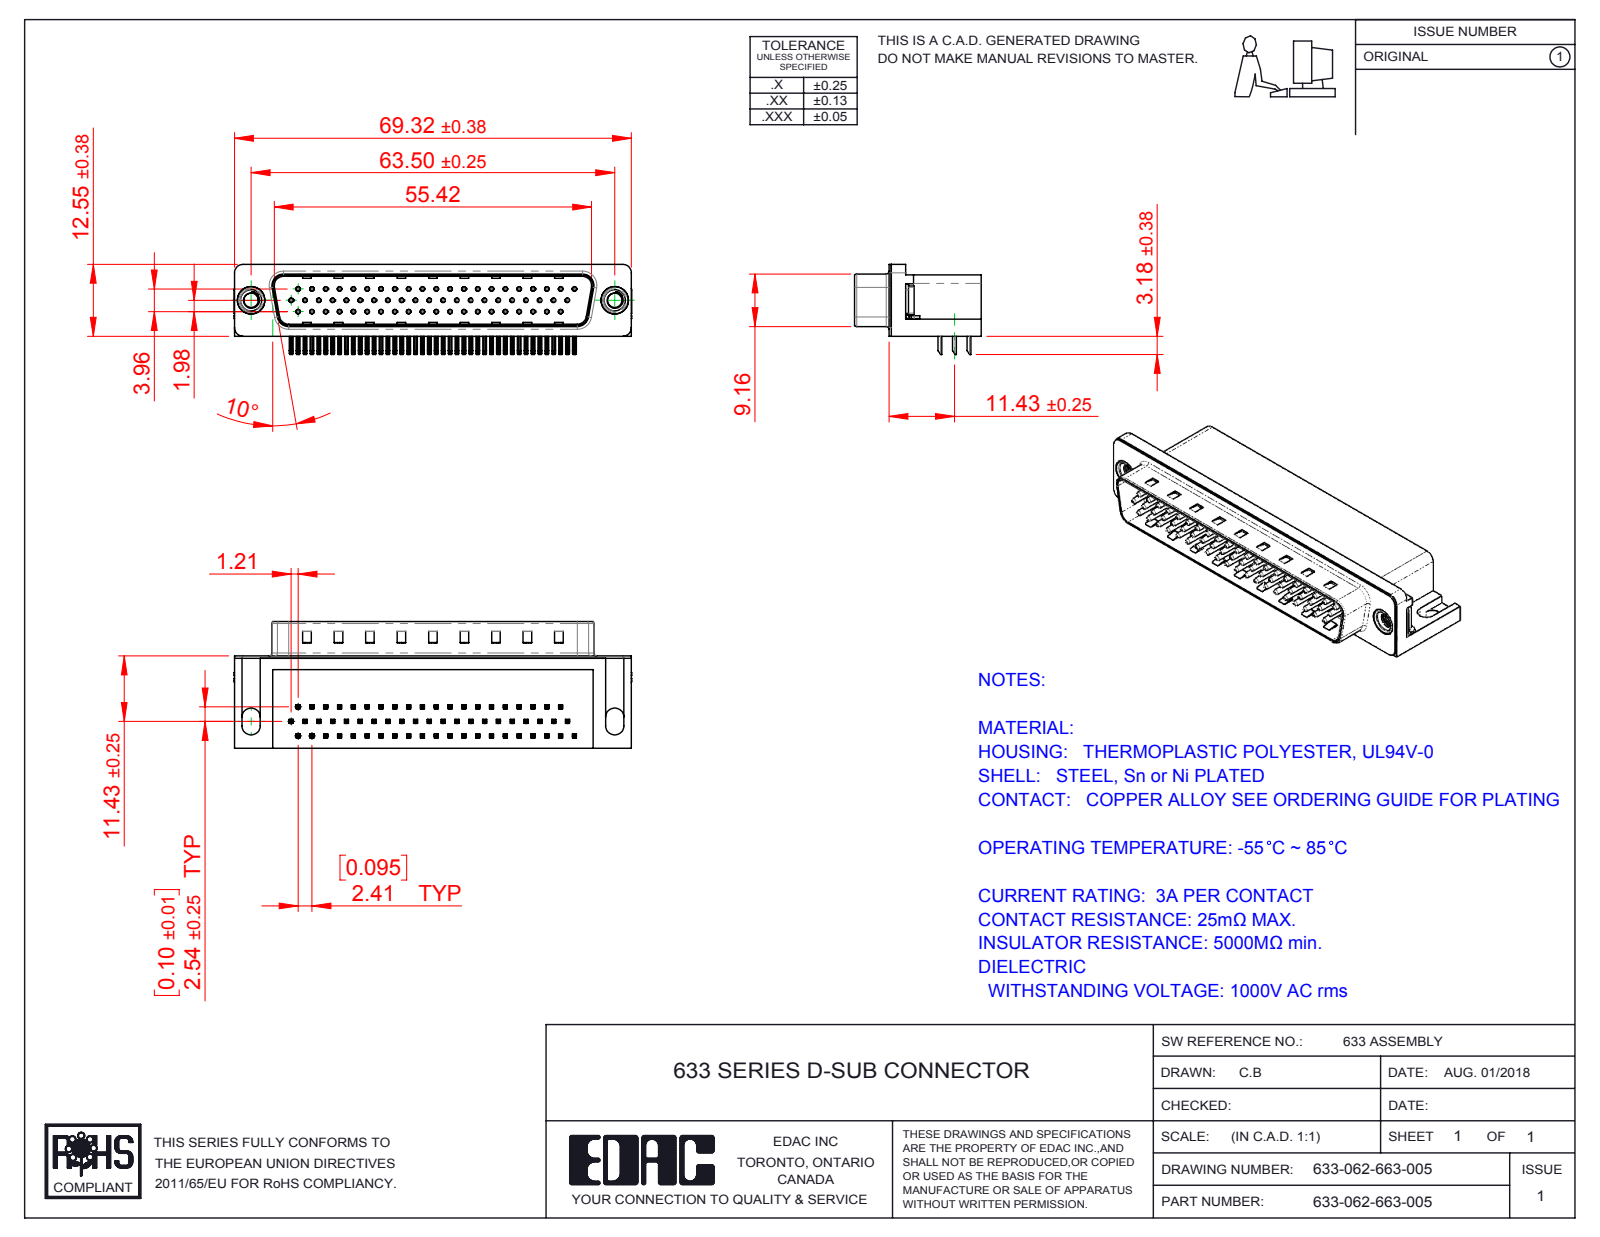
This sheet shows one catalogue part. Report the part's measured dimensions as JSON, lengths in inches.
{"part_name": "633 Housing_62 Contact; 633 M3 Threaded Rivet; 633-062-663-005; 633 Contact Bottom (+4 more)", "step_written_by": "SolidWorks 2016 (CONFIG_CONTROL_DESIGN)", "units": "inches", "bodies": {"solids": 68, "faces": 5072, "planar": 3213, "cylindrical": 1442, "other": 417}, "overall_size": [2.732, 0.87, 0.619], "volume_in3": 0.671, "surface_area_in2": 20.44, "round_holes": [[0.014, 62], [0.031, 62], [0.098, 2], [0.157, 2], [0.189, 2], [0.197, 2]], "round_bosses_or_shafts": [[0.03, 62], [0.193, 2], [0.187, 2], [0.154, 2]], "partial_cylinders_radius": [[0.01, 256], [0.005, 124], [0.039, 16], [0.02, 9], [0.063, 8], [0.059, 7], [0.035, 4], [0.079, 4]], "face_to_face_distances": [0.016, 0.407, 0.618, 0.345, 0.098, 0.1, 0.114, 0.329, 0.083, 0.339], "hole_center_spacings": [0.095, 0.19, 0.285, 0.38, 0.57, 0.665, 0.19, 0.285]}
